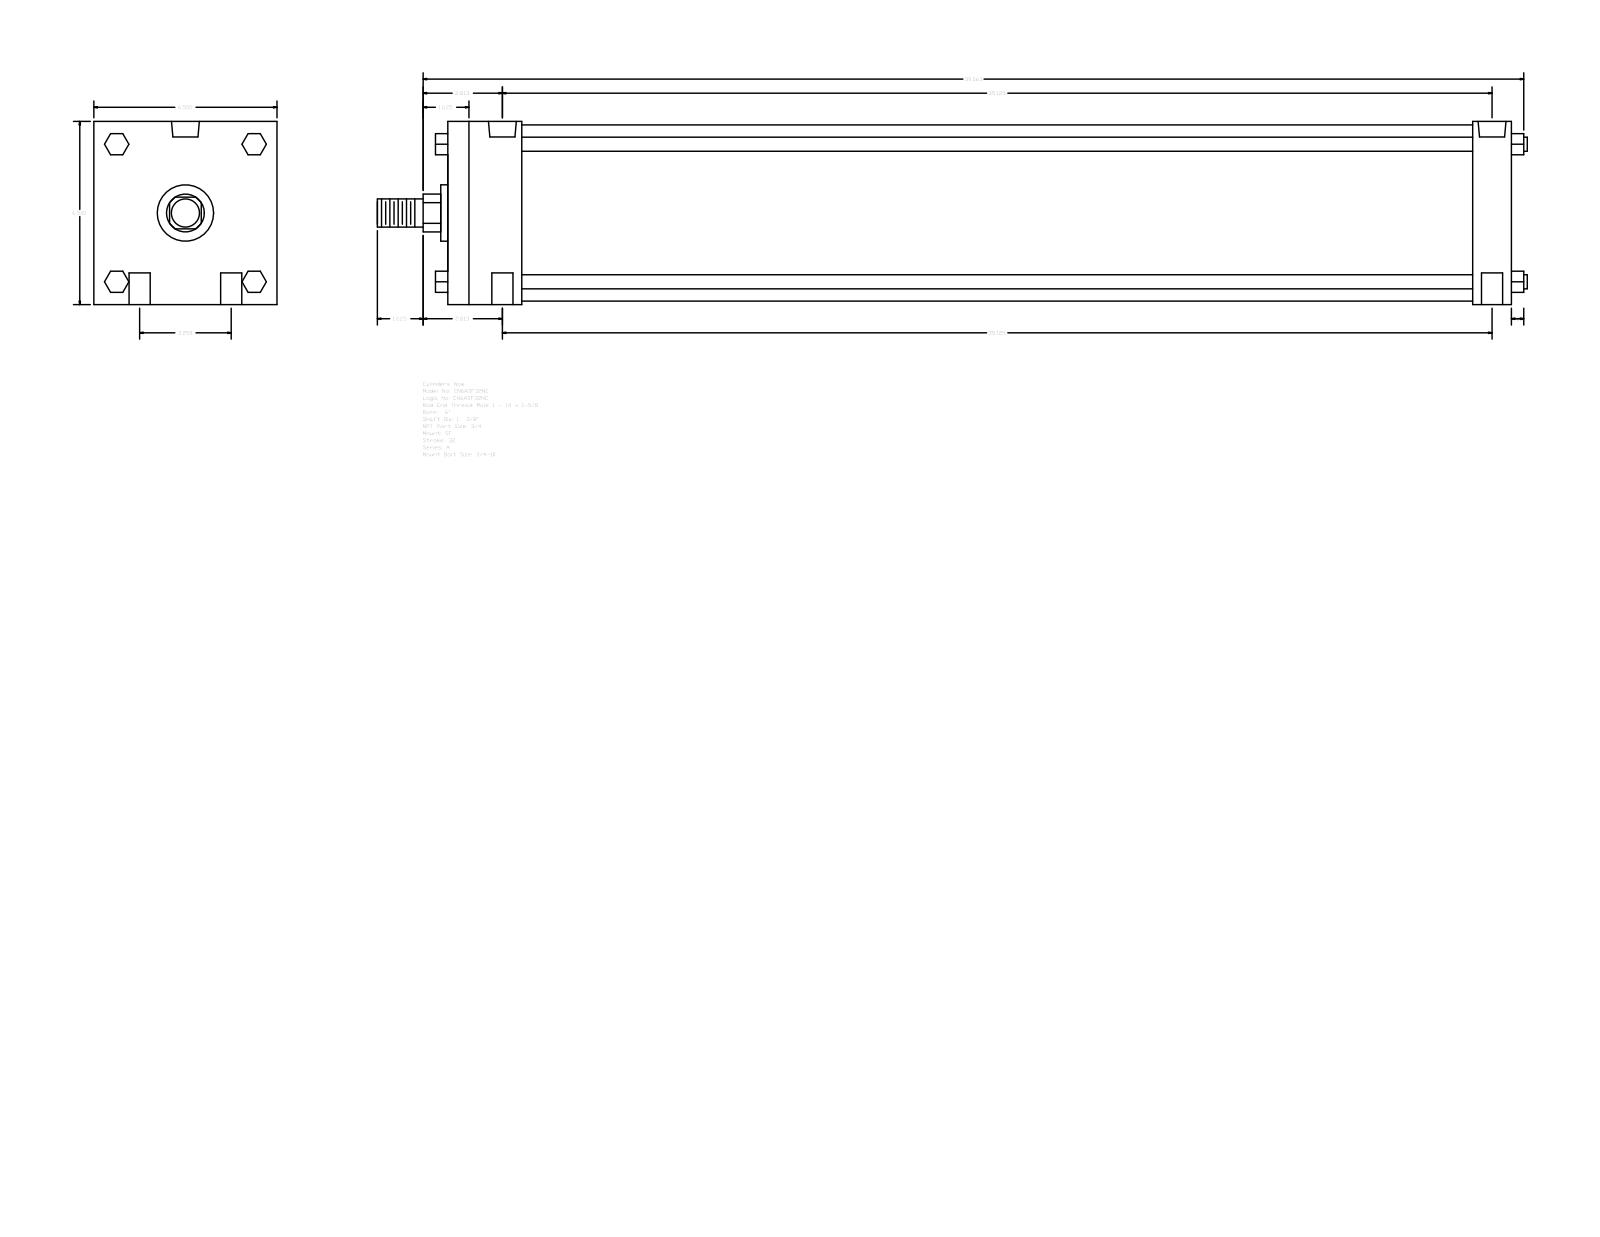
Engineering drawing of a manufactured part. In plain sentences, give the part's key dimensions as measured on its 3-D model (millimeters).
The part is named "A_SF__0600_1.375". Its 3-D file was written by "GSSL Pune (CONFIG_CONTROL_DESIGN)". It is 0 solids with 124 faces: 94 planar, 30 cylindrical and 0 other. Overall it measures 1036.64 by 165.1 by 165.1 millimeters. Round holes: 4 of diameter 19.05, 2 of diameter 15.08, 2 of diameter 25.12. Round bosses or shafts: 4 of diameter 12.7, 1 of diameter 158.75, 1 of diameter 50.8, 1 of diameter 34.92, 1 of diameter 25.4. Partial cylindrical surfaces (rounded edges, fillets, slot ends): 1 of radius 17.06. The main face-to-face distances are 165.1, 958.85, 923.92, 34.93, 66.67, 857.25, 892.18, 19.05, 61.97, 107.34. The hole center spacings are 41.27, 893.12, 892.17, 82.54, 895.98, 881.05.
